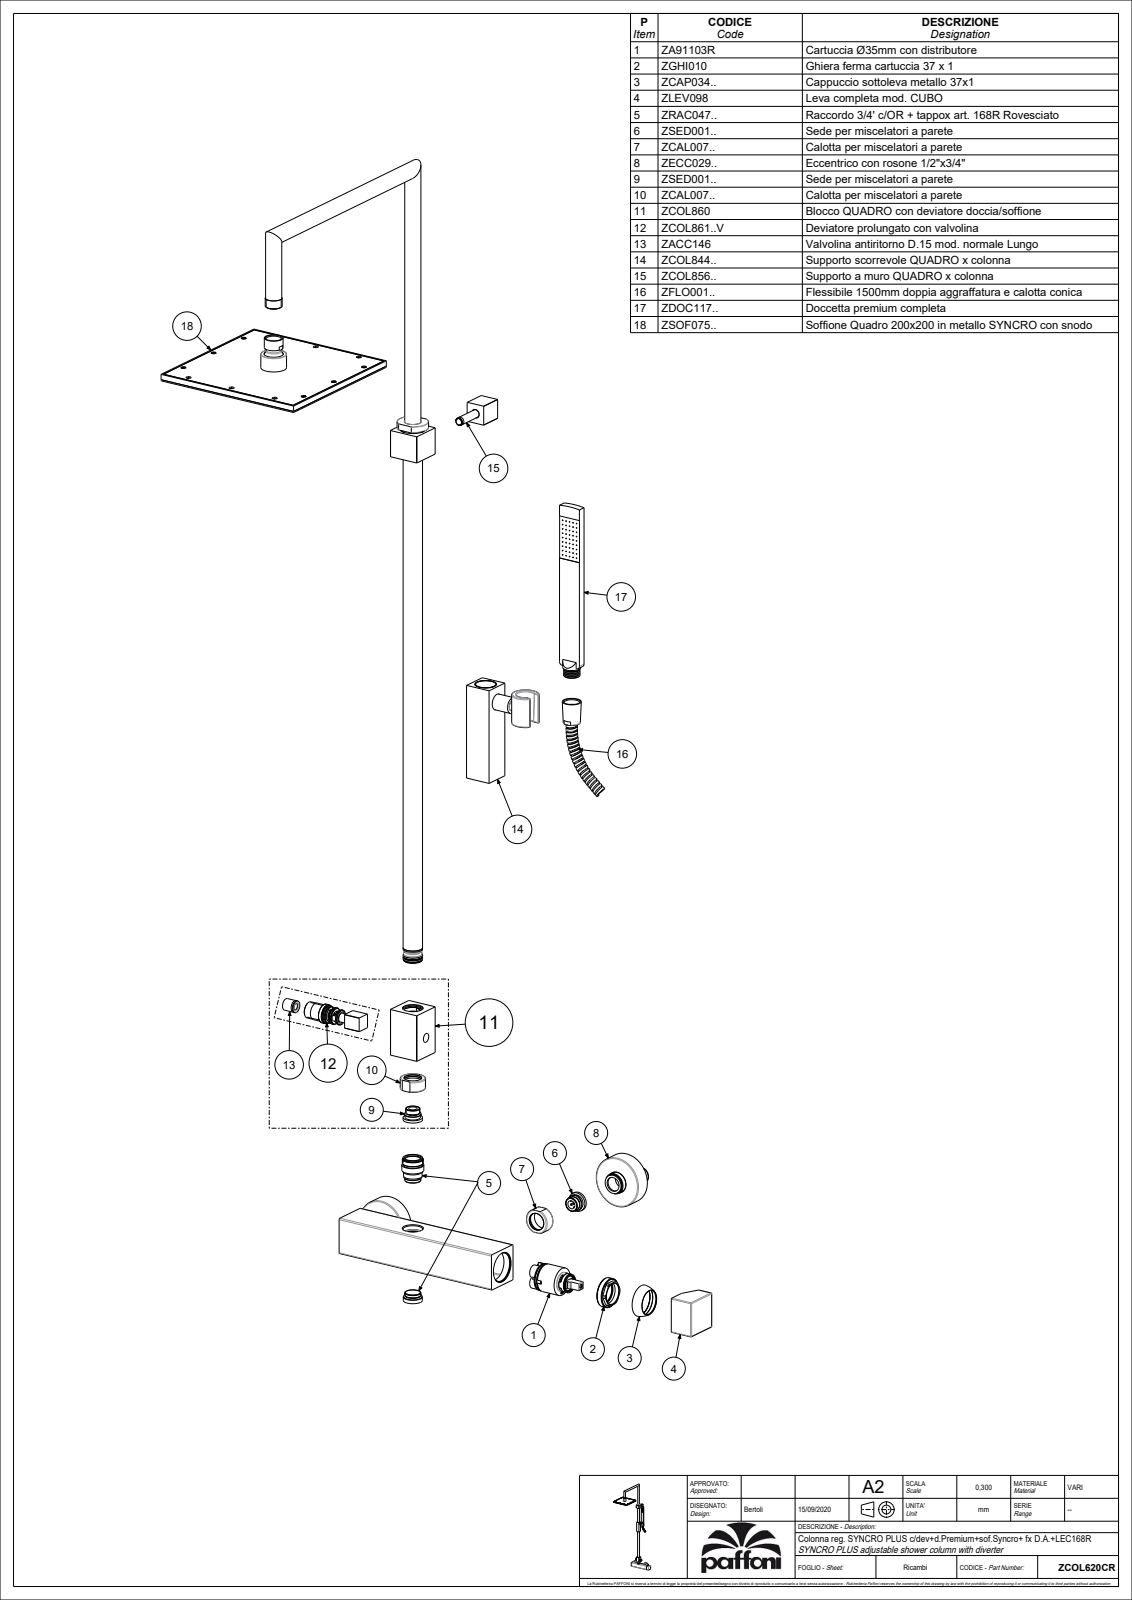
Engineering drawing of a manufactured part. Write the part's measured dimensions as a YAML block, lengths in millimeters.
part_name: "ZCOL620CR"
step_written_by: "CREO PARAMETRIC BY PTC INC, 2020044 (CONFIG_CONTROL_DESIGN)"
units: millimeters
bodies: {solids: 10, faces: 7165, planar: 1639, cylindrical: 1482, other: 4044}
overall_size: [1100.5, 480.1, 272.75]
volume: 944995
surface_area: 673558
round_holes:
  - {diameter: 1.5, count: 100}
  - {diameter: 1.7, count: 100}
  - {diameter: 7, count: 15}
  - {diameter: 2.5, count: 12}
  - {diameter: 5.1, count: 12}
  - {diameter: 6, count: 12}
  - {diameter: 5, count: 5}
  - {diameter: 10.5, count: 5}
  - {diameter: 3.3, count: 4}
  - {diameter: 9, count: 4}
  - {diameter: 25, count: 4}
  - {diameter: 12, count: 3}
round_bosses_or_shafts:
  - {diameter: 10, count: 101}
  - {diameter: 5, count: 13}
  - {diameter: 2, count: 11}
  - {diameter: 20, count: 4}
  - {diameter: 24, count: 3}
  - {diameter: 63.5, count: 2}
  - {diameter: 27, count: 2}
  - {diameter: 17.7, count: 2}
partial_cylinders:
  - {radius: 1, count: 106}
  - {radius: 0.5, count: 44}
  - {radius: 20, count: 12}
  - {radius: 0.15, count: 11}
  - {radius: 0.3, count: 9}
  - {radius: 1.5, count: 4}
  - {radius: 7, count: 4}
  - {radius: 12, count: 4}
face_to_face_distances: [8.5, 7.5, 1, 42.75, 3.75, 7, 3, 6, 1.5, 46.5]
hole_center_spacings: [16.3, 23.05, 36.45, 51.55, 32.6, 67.21, 48.9, 65.2]
